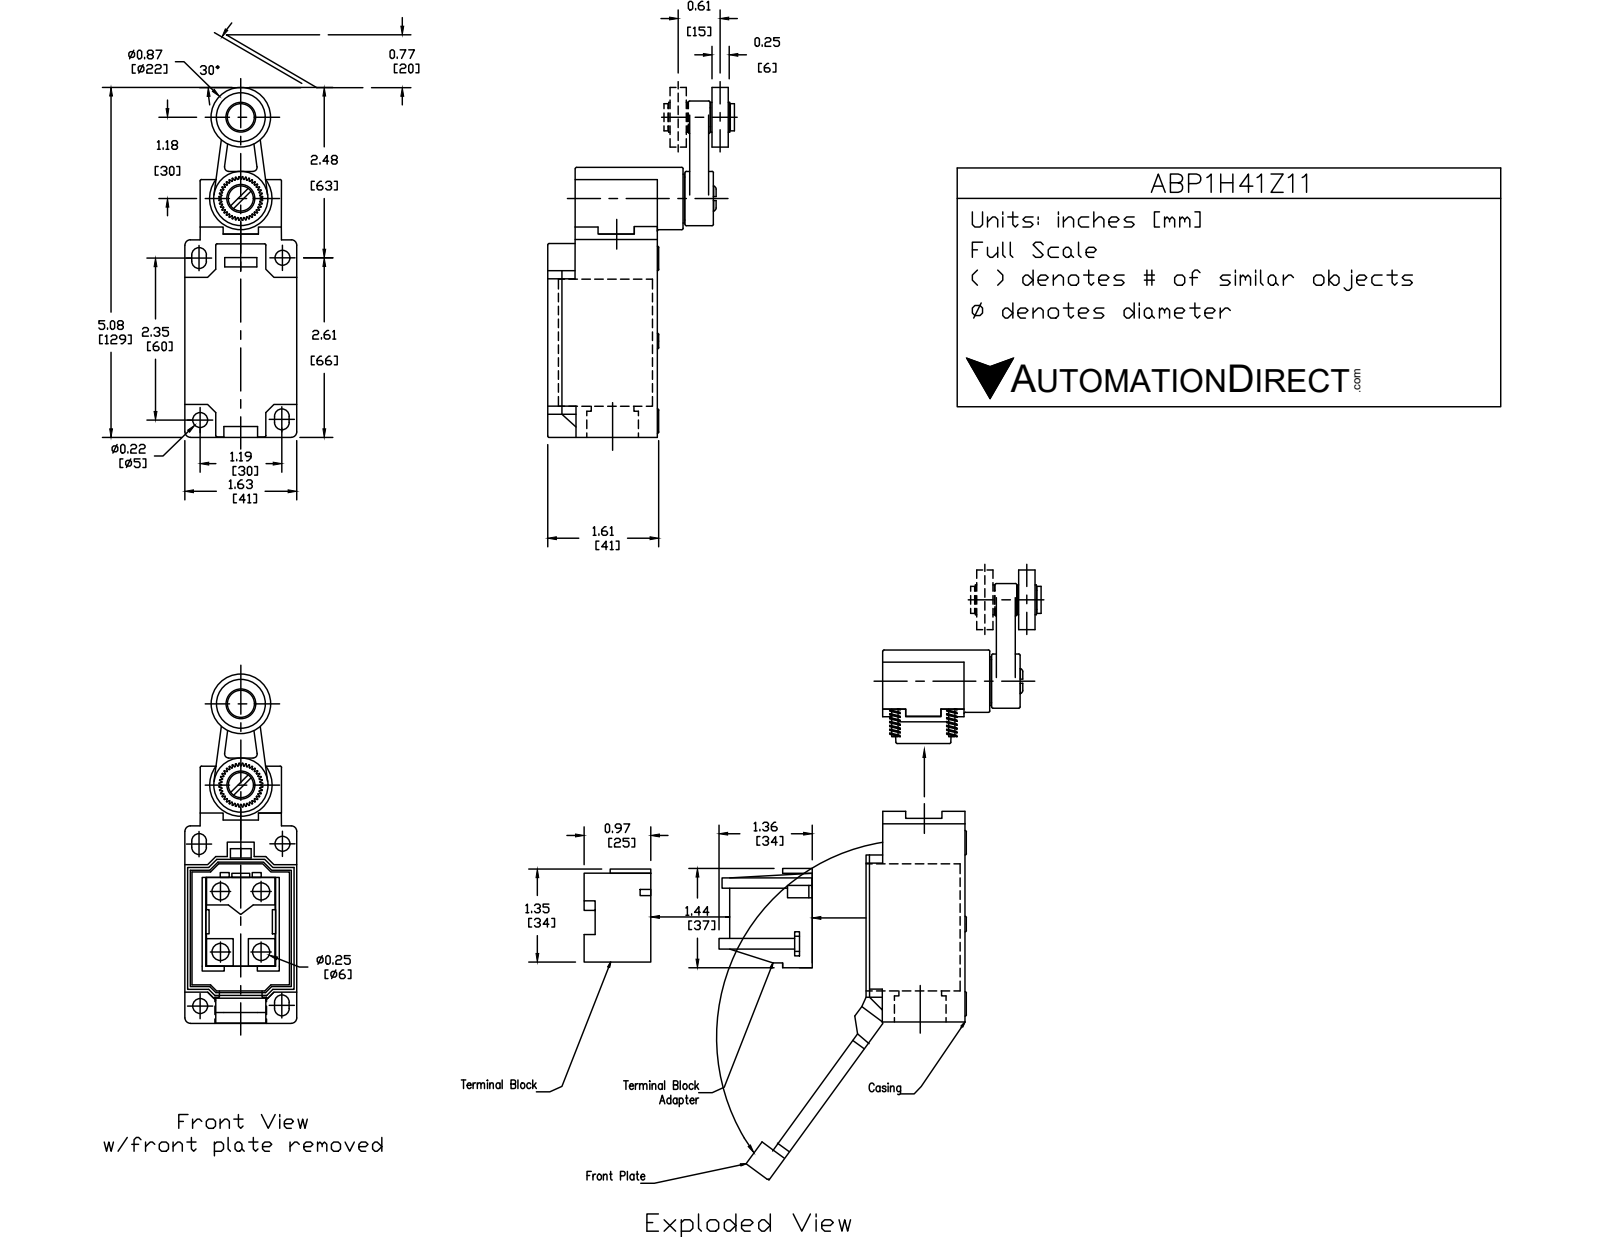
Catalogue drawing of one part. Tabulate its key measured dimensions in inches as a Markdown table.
| quantity | value |
| --- | --- |
| part name | ABP1H41Z11 |
| STEP written by | SolidWorks 2017 (AUTOMOTIVE_DESIGN) |
| units | inches |
| bodies | 5 solids, 193 faces (86 planar, 81 cylindrical, 26 other) |
| overall size | 5.091 × 2.313 × 1.614 |
| volume | 8.635 in³ |
| surface area | 42.99 in² |
| round holes (diameter × count) | 0.213 × 2, 0.551 × 1, 0.669 × 1, 0.748 × 1 |
| round bosses / shafts (diameter × count) | 0.354 × 5, 0.394 × 2, 0.906 × 1, 0.866 × 1, 0.787 × 1, 0.709 × 1, 0.276 × 1 |
| partial cylindrical surfaces (radius × count) | 0.02 × 16, 0.079 × 4, 0.106 × 4, 0.236 × 1, 0.453 × 1, 0.472 × 1 |
| main face-to-face distances | 1.614, 1.565, 1.181, 0.217, 1.398, 2.972, 0.069, 0.384, 0.138, 0.354 |
| hole center spacings | 1.042, 2.641, 3.274 |
